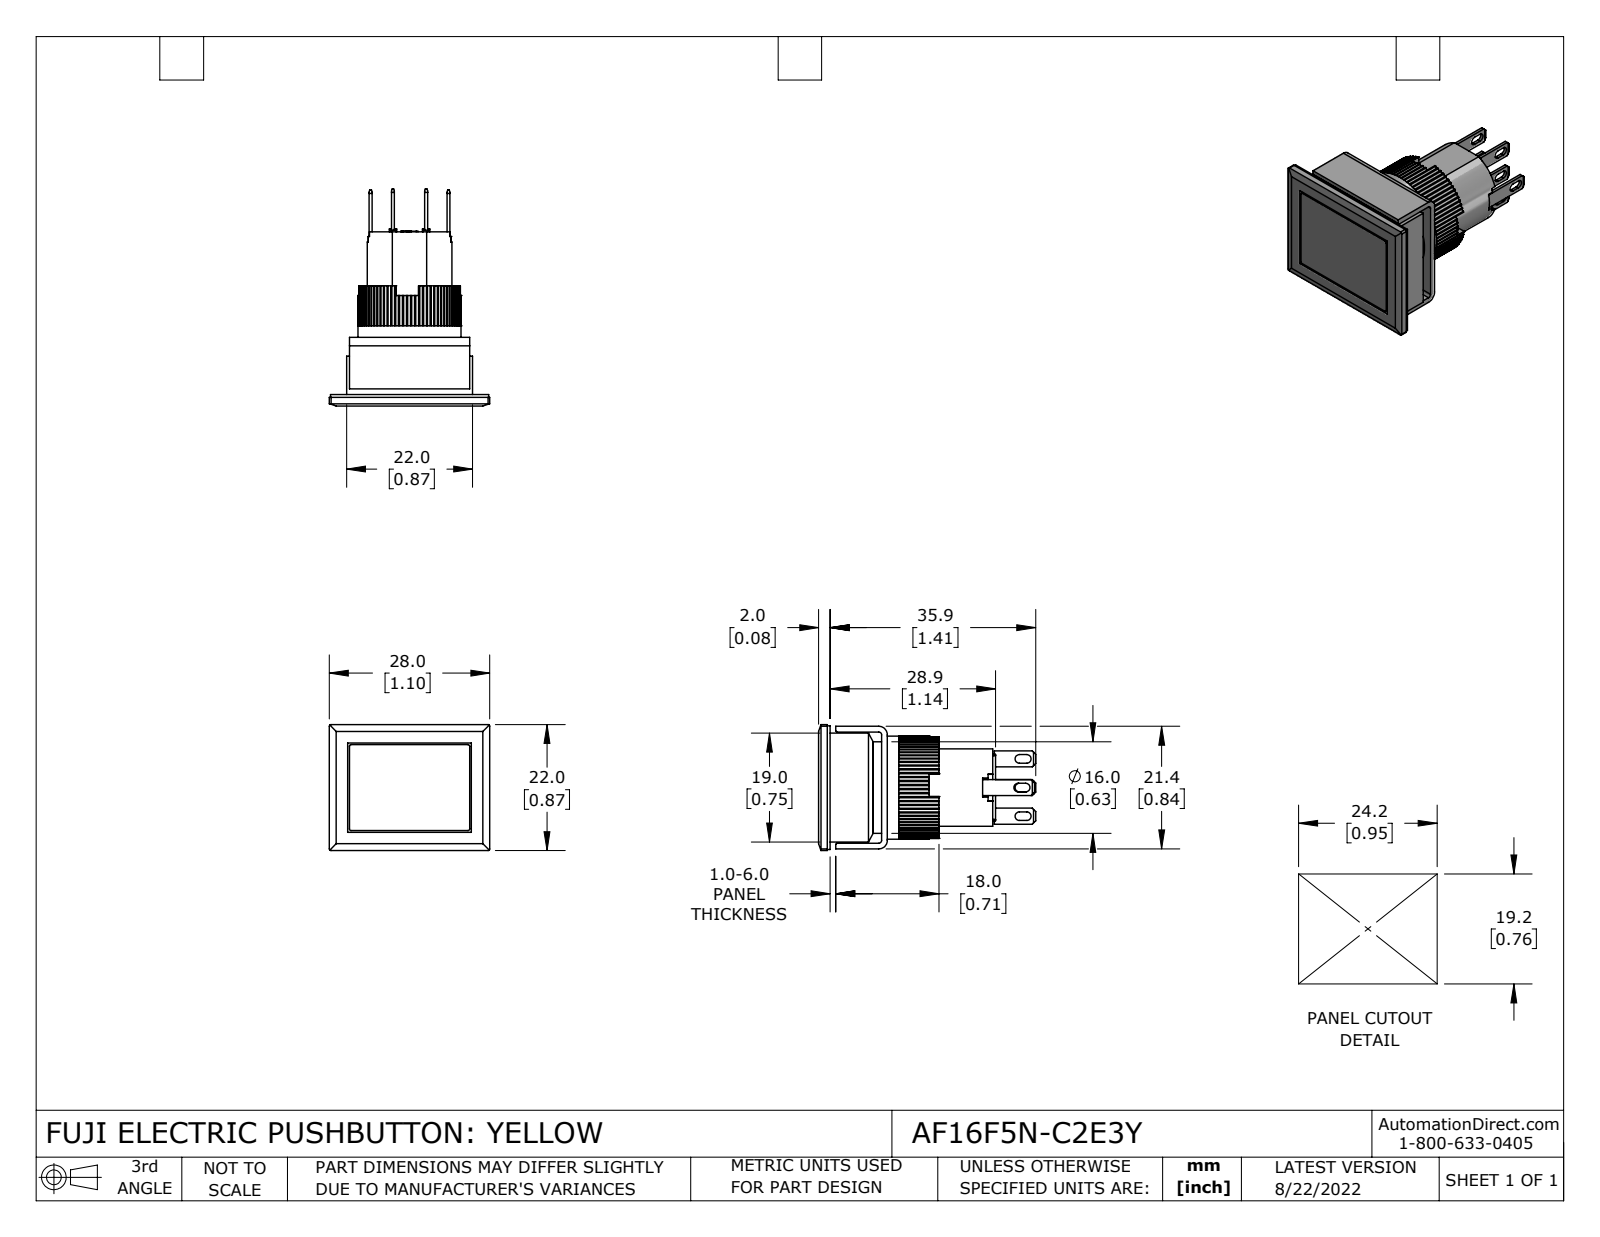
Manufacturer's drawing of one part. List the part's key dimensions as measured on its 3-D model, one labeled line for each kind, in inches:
Part name (STEP PRODUCT): AF16F5N-C2E3Y
STEP written by: SolidWorks 2021 (CONFIG_CONTROL_DESIGN)
Units: inches
Bodies: 14 solids, 828 faces (644 planar, 182 cylindrical, 2 other)
Overall size (bounding box): 1.492 × 1.102 × 0.866
Volume: 0.543 in³ · Surface area: 12.03 in²
Round holes (diameter × count): ⌀0.039 ×1, ⌀0.709 ×1
Round bosses / shafts (diameter × count): ⌀0.63 ×1, ⌀0.583 ×1
Partial cylindrical surfaces — rounded edges, fillets, slot ends (radius × count): R0.01 ×80, R0.008 ×12, R0.012 ×8, R0.03 ×8, R0.02 ×2, R0.059 ×2
Main face-to-face distances: 0.374, 0.059, 0.02, 0.142, 0.039, 0.315, 0.232, 0.083, 0.079, 0.756
